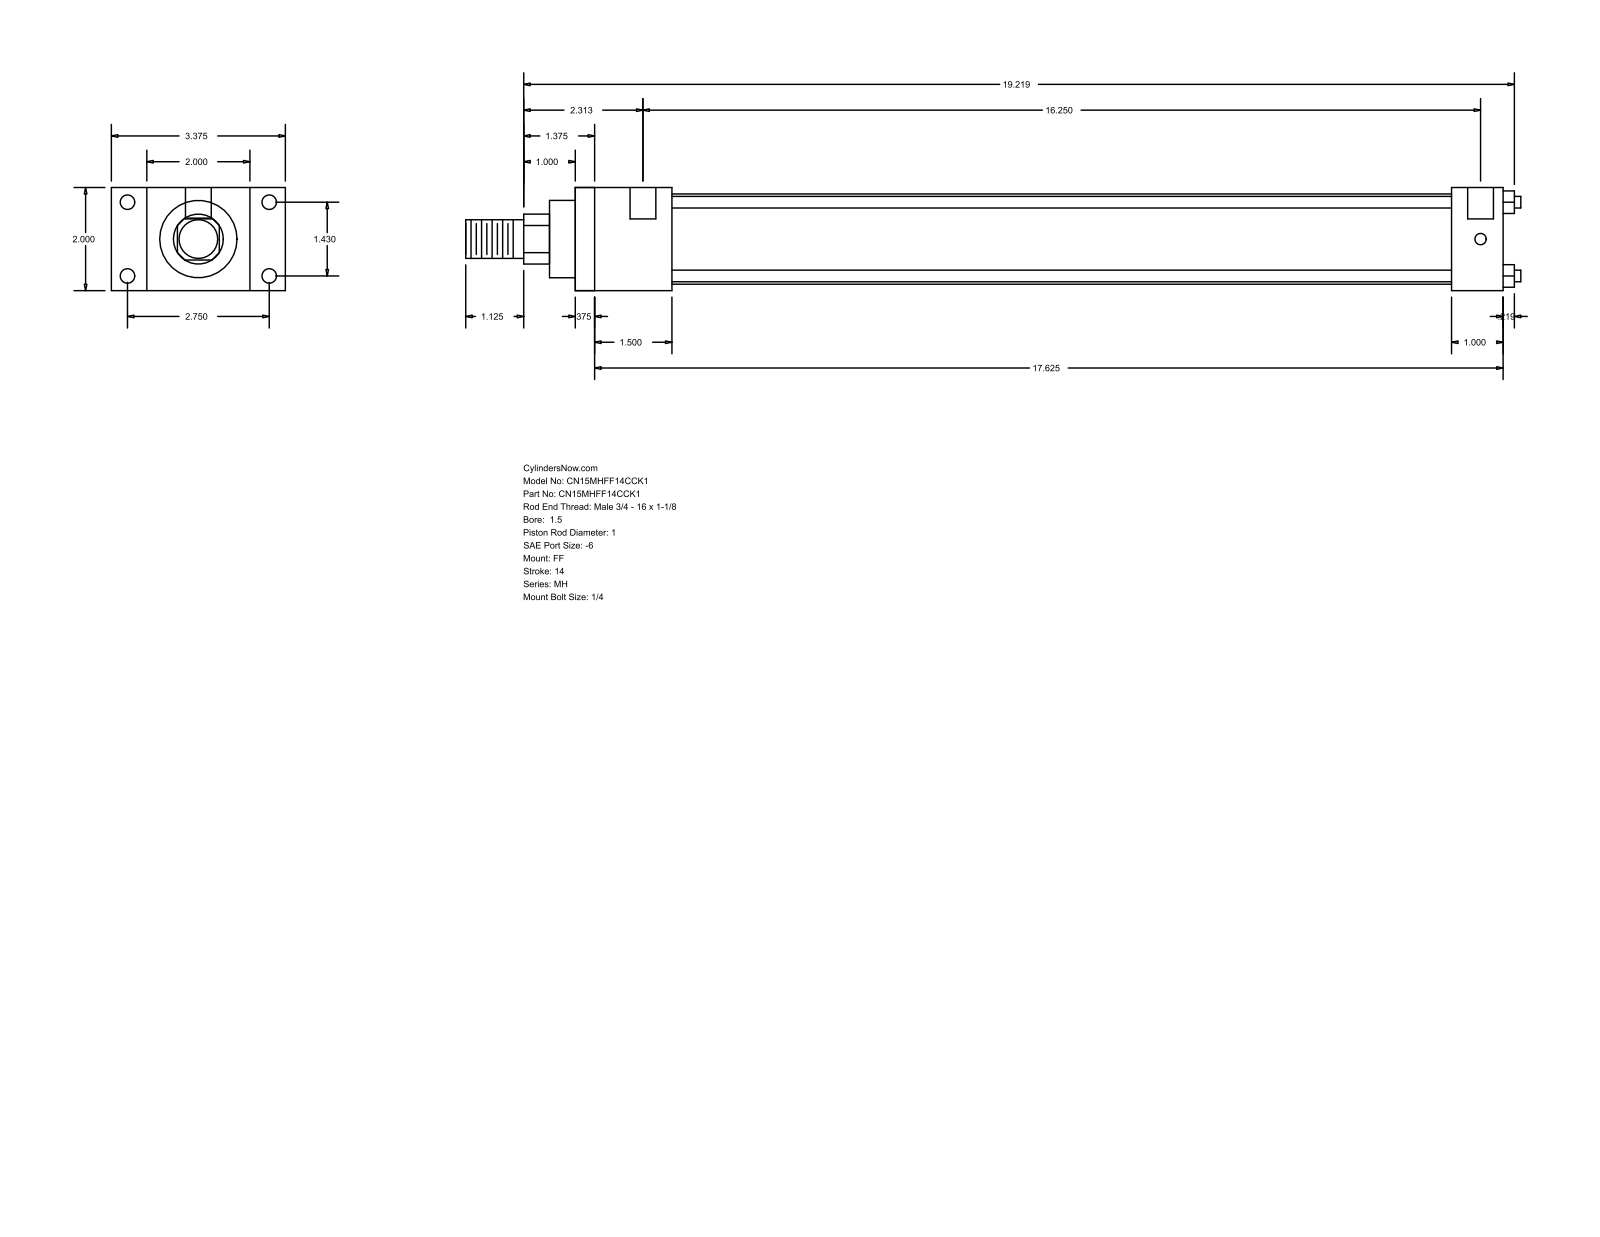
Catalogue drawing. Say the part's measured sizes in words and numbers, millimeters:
The part is named "MH_FF__0150_1". Its 3-D file was written by "GSSL Pune (CONFIG_CONTROL_DESIGN)". It is 0 solids with 92 faces: 64 planar, 28 cylindrical and 0 other. Overall it measures 519.91 by 85.72 by 50.8 millimeters. Round holes: 4 of diameter 5.56, 4 of diameter 7.14, 2 of diameter 12.7. Round bosses or shafts: 4 of diameter 5.71, 1 of diameter 44.45, 1 of diameter 38.1, 1 of diameter 25.4, 1 of diameter 19.05. Partial cylindrical surfaces (rounded edges, fillets, slot ends): 1 of radius 12.29. The main face-to-face distances are 50.8, 457.2, 9.52, 447.68, 25.4, 17.46, 68.26, 47.63, 38.11, 409.57. The hole center spacings are 36.32, 69.84, 78.72, 415.93, 3.18, 412.75.
